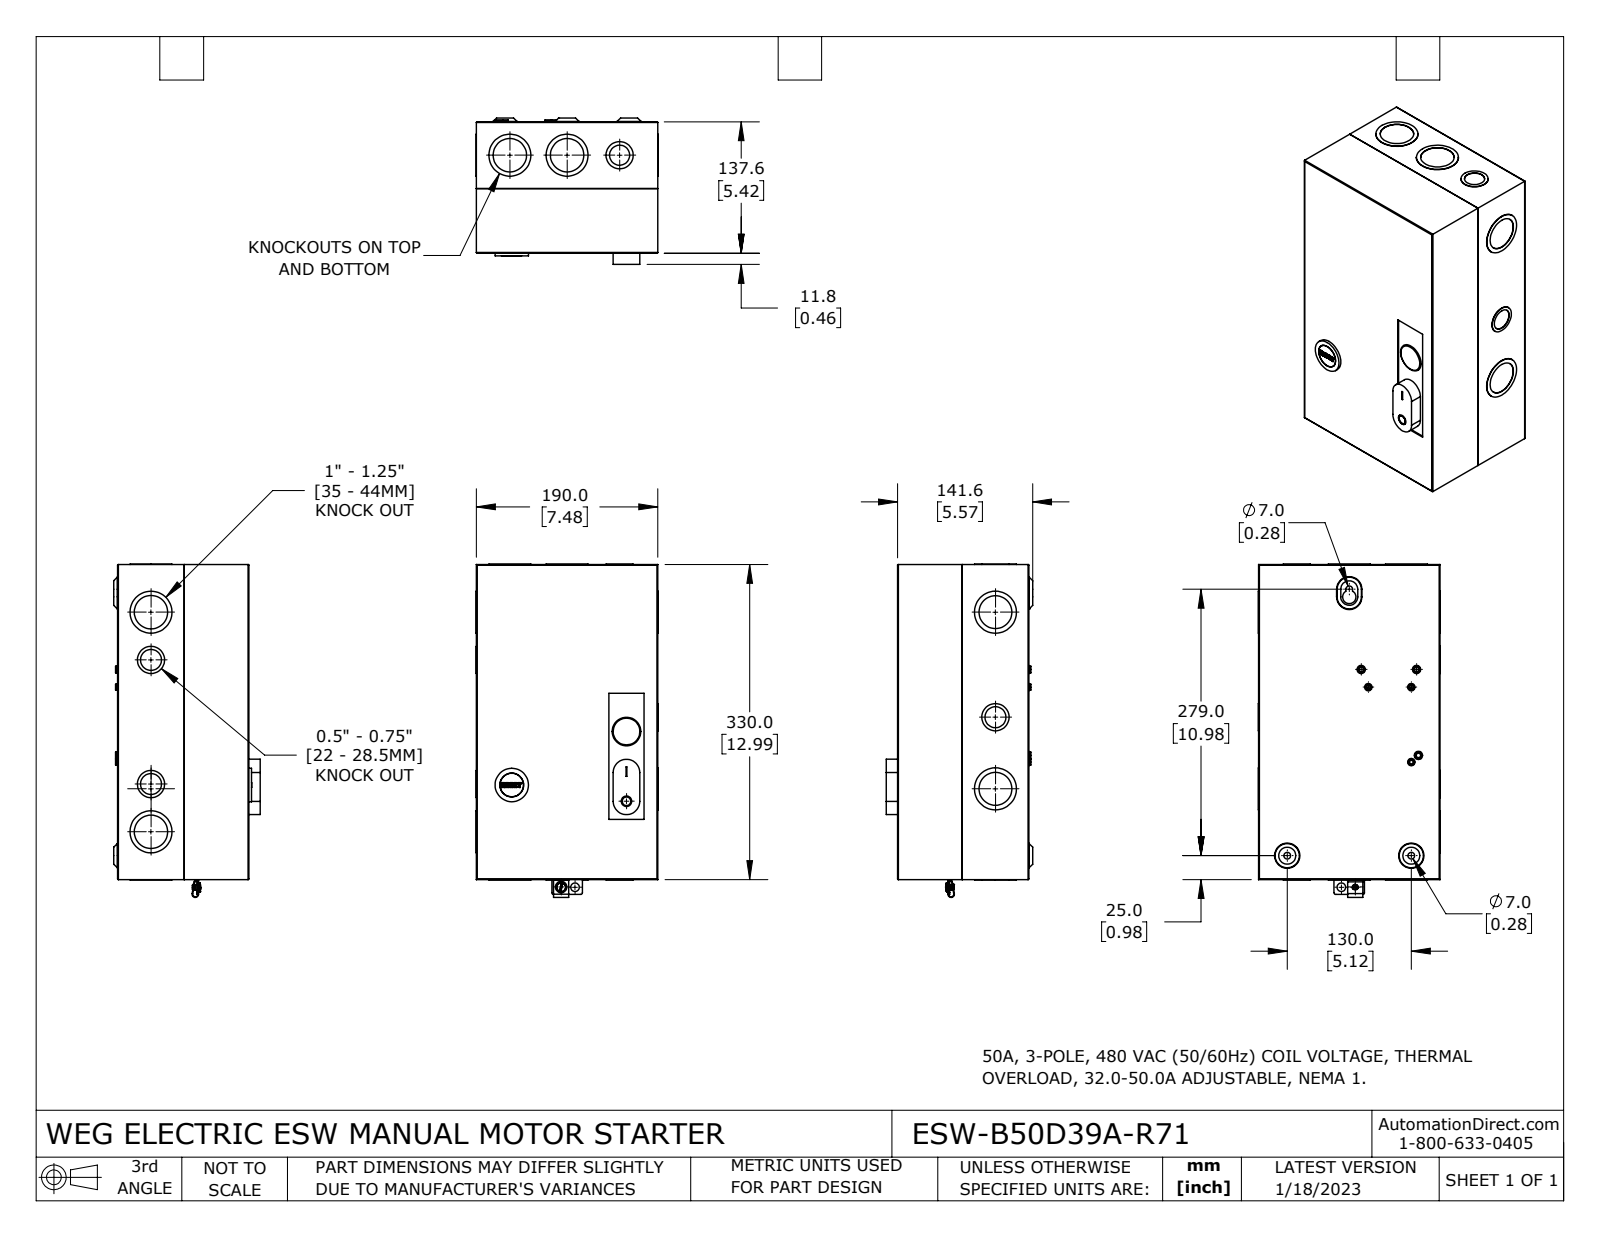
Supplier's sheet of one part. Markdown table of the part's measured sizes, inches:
| quantity | value |
| --- | --- |
| part name | ESW-B50D39A-R71 |
| STEP written by | SolidWorks 2021 (CONFIG_CONTROL_DESIGN) |
| units | inches |
| bodies | 7 solids, 435 faces (161 planar, 221 cylindrical, 53 other) |
| overall size | 13.74 × 7.504 × 6.039 |
| volume | 24.58 in³ |
| surface area | 936.7 in² |
| round holes (diameter × count) | 1.378 × 4, 0.146 × 3, 0.183 × 3, 0.276 × 2, 0.866 × 2, 0.886 × 2, 1.357 × 2, 0.256 × 1, 0.279 × 1, 0.354 × 1, 0.433 × 1, 0.469 × 1 |
| round bosses / shafts (diameter × count) | 1.732 × 4, 1.122 × 3, 0.278 × 3, 0.24 × 3, 1.734 × 2, 1.378 × 1, 1.193 × 1, 1.148 × 1 |
| partial cylindrical surfaces (radius × count) | 0.004 × 34, 0.031 × 8, 0.079 × 3, 0.138 × 3, 0.059 × 2, 0.075 × 2, 0.108 × 2, 0.122 × 2 |
| main face-to-face distances | 0.047, 5.37, 7.433, 5.323, 5.417, 12.945, 7.386, 7.48, 0.071, 12.898 |
| hole center spacings | 0.571, 1.772, 1.969, 2.283, 2.362, 5.118, 7.087, 10.972 |
